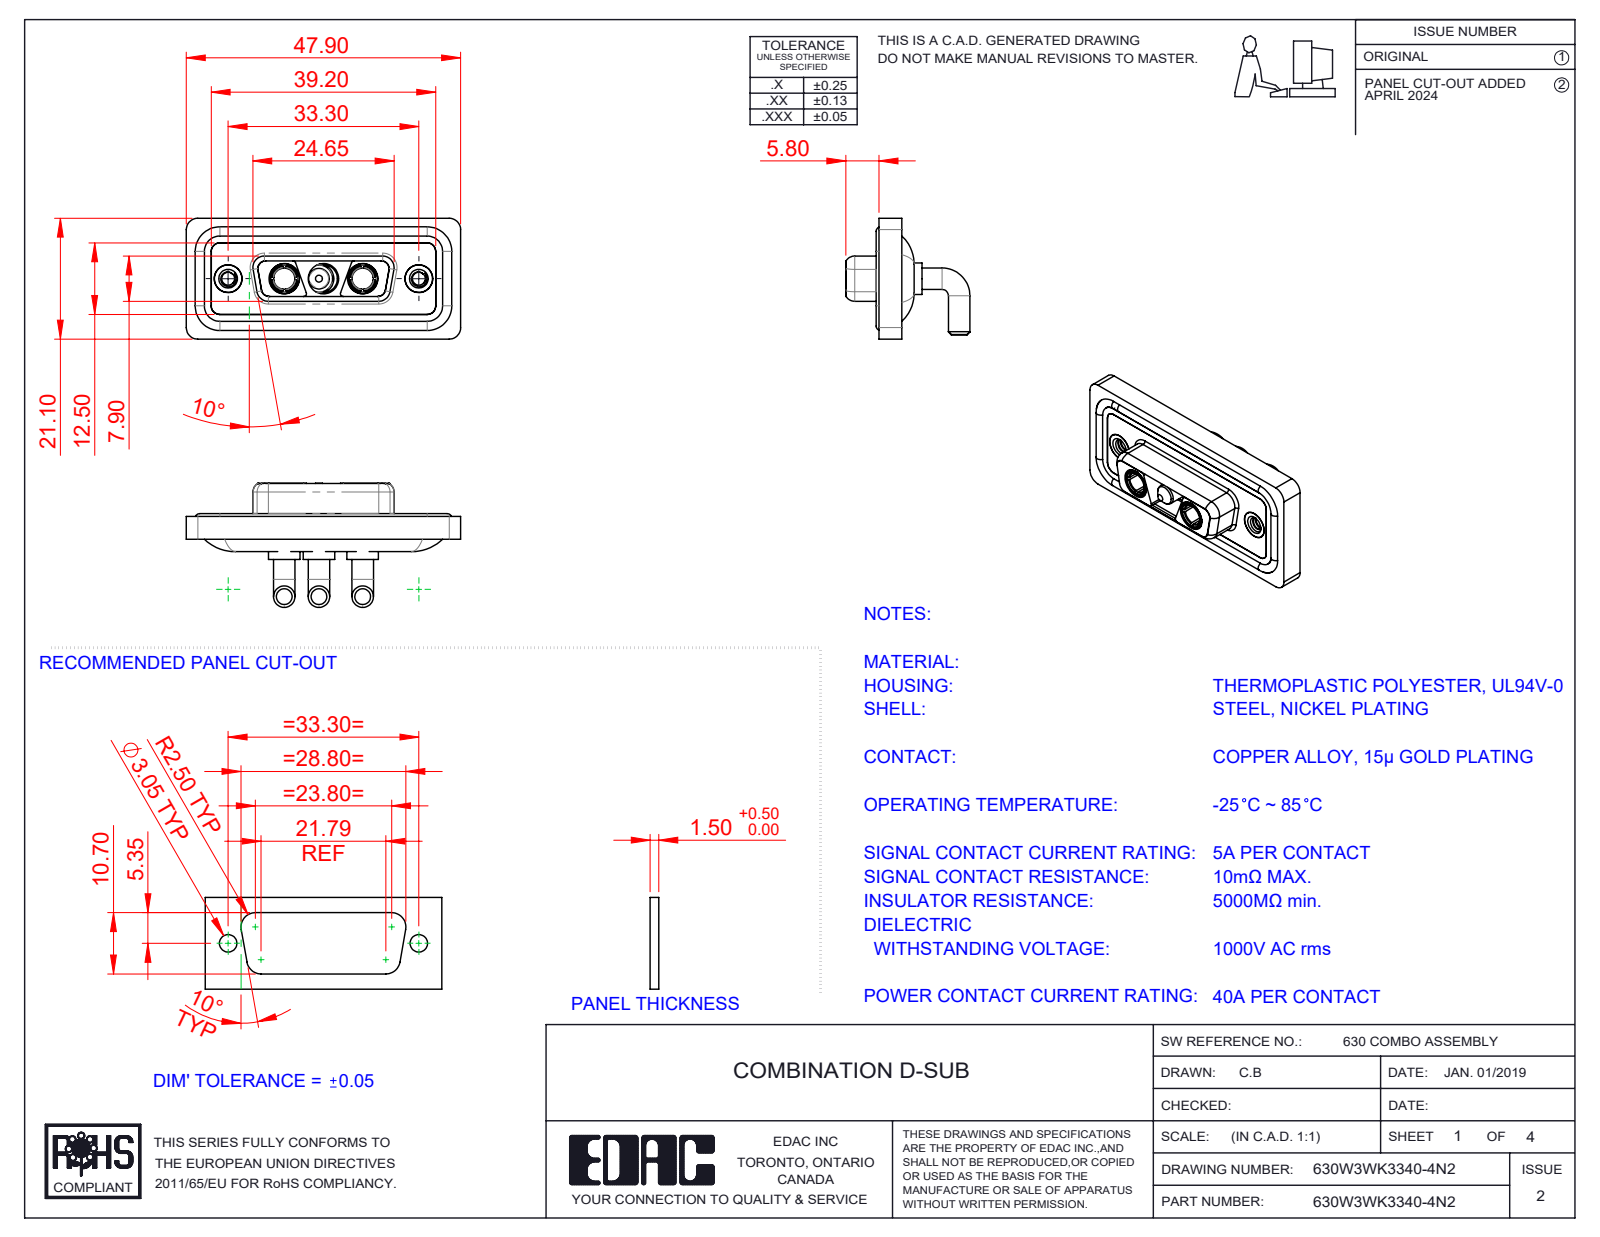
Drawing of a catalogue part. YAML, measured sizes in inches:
part_name: "630Combo Housing_3WK3; 630W3WK3340-4N2; 630Combo Shell Rear_15 Contacts; Power Socket_40A RA (+4 more)"
step_written_by: "SolidWorks 2023 (CONFIG_CONTROL_DESIGN)"
units: inches
bodies: {solids: 13, faces: 595, planar: 178, cylindrical: 264, other: 153}
overall_size: [1.886, 0.854, 0.831]
volume: 0.381
surface_area: 15.3
round_holes:
  - {diameter: 0.191, count: 5}
  - {diameter: 0.209, count: 3}
  - {diameter: 0.089, count: 2}
  - {diameter: 0.146, count: 2}
  - {diameter: 0.157, count: 2}
  - {diameter: 0.159, count: 2}
  - {diameter: 0.197, count: 2}
round_bosses_or_shafts:
  - {diameter: 0.148, count: 6}
  - {diameter: 0.063, count: 4}
  - {diameter: 0.217, count: 3}
  - {diameter: 0.205, count: 3}
  - {diameter: 0.187, count: 3}
  - {diameter: 0.195, count: 2}
  - {diameter: 0.195, count: 2}
  - {diameter: 0.189, count: 2}
partial_cylinders:
  - {radius: 0.079, count: 20}
  - {radius: 0.059, count: 18}
  - {radius: 0.053, count: 12}
  - {radius: 0.02, count: 8}
  - {radius: 0.063, count: 8}
  - {radius: 0.01, count: 4}
  - {radius: 0.024, count: 4}
  - {radius: 0.026, count: 4}
face_to_face_distances: [0.016, 0.071, 0.043, 0.063, 0.114, 0.098, 0.122, 0.146, 0.161, 0.059]
hole_center_spacings: [0.27, 0.386, 0.656, 0.925, 0.539, 1.311]
